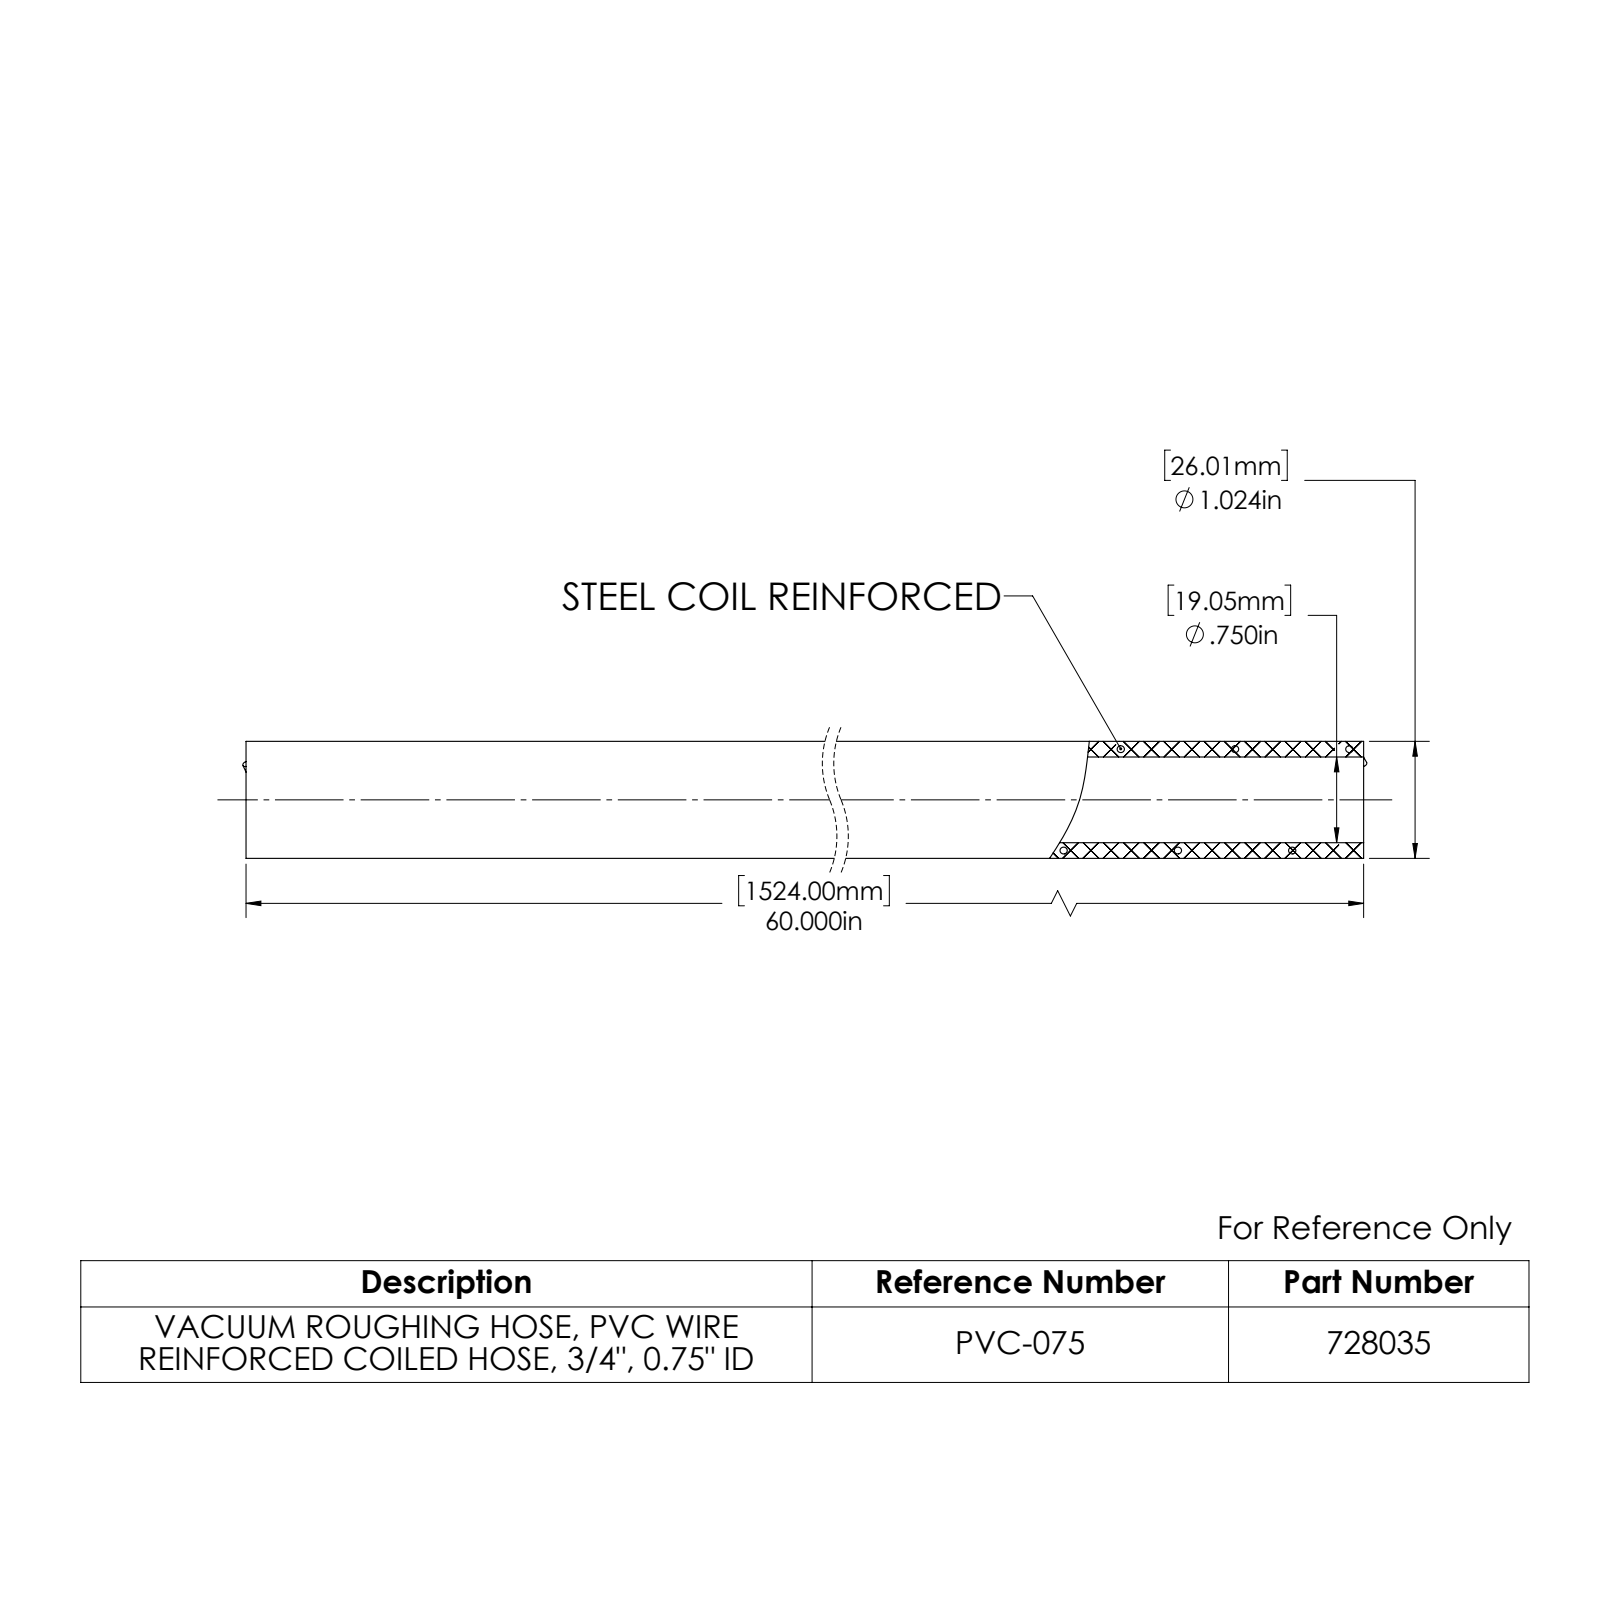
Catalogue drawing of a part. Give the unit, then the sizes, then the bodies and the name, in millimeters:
Units: millimetres
Overall size (bounding box): 1524 × 22.4 × 22.4
Round holes (diameter × count): ⌀19.1 ×1
Round bosses / shafts (diameter × count): ⌀22.4 ×1
Main face-to-face distances: 1524
Volume: 163 600 mm³ · Surface area: 198 500 mm²
Bodies: 1 solid, 6 faces (2 planar, 4 cylindrical, 0 other)
Part name (STEP PRODUCT): 728035
STEP written by: SolidWorks 2022 (AUTOMOTIVE_DESIGN)
